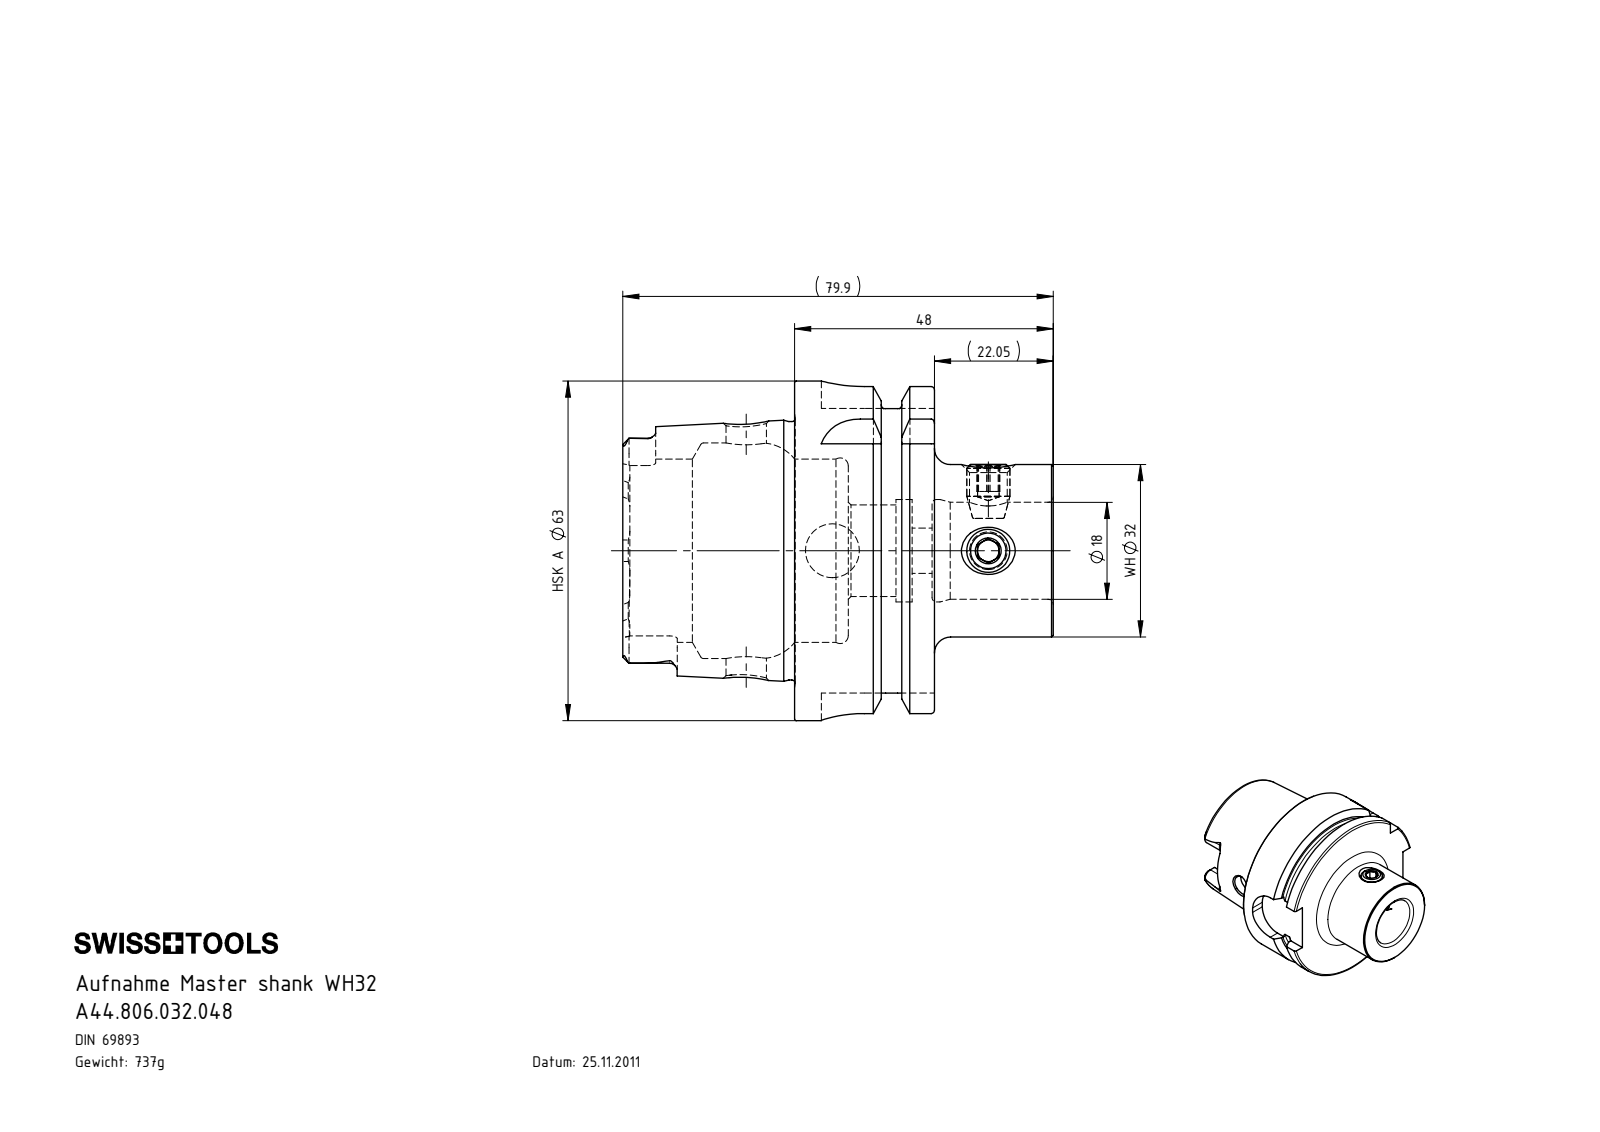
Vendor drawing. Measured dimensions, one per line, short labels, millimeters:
name: WH3-ER1.001.010; HA6-WH3.K01.048; HA6-WH3.K01.048_A
written by: SolidWorks 2015 (AUTOMOTIVE_DESIGN)
unit: mm
bodies: 4 solids, 230 faces (74 planar, 59 cylindrical, 97 other)
size: 79.9 × 63 × 63
volume: 93 977 mm³; area: 26 835 mm²
holes: 2× ⌀7, 1× ⌀7.5, 1× ⌀8.4, 1× ⌀10, 1× ⌀17, 1× ⌀18, 1× ⌀19, 1× ⌀34, 1× ⌀40
bosses: 2× ⌀8, 1× ⌀63, 1× ⌀54.95, 1× ⌀47.94, 1× ⌀32
rounds: 6× R1.4, 4× R2.88, 4× R8
face distances: 25.95, 16, 9.95, 48, 38.05, 22.05, 31.9, 41.85, 57.85, 79.9
hole spacings: 28.95, 44.95
